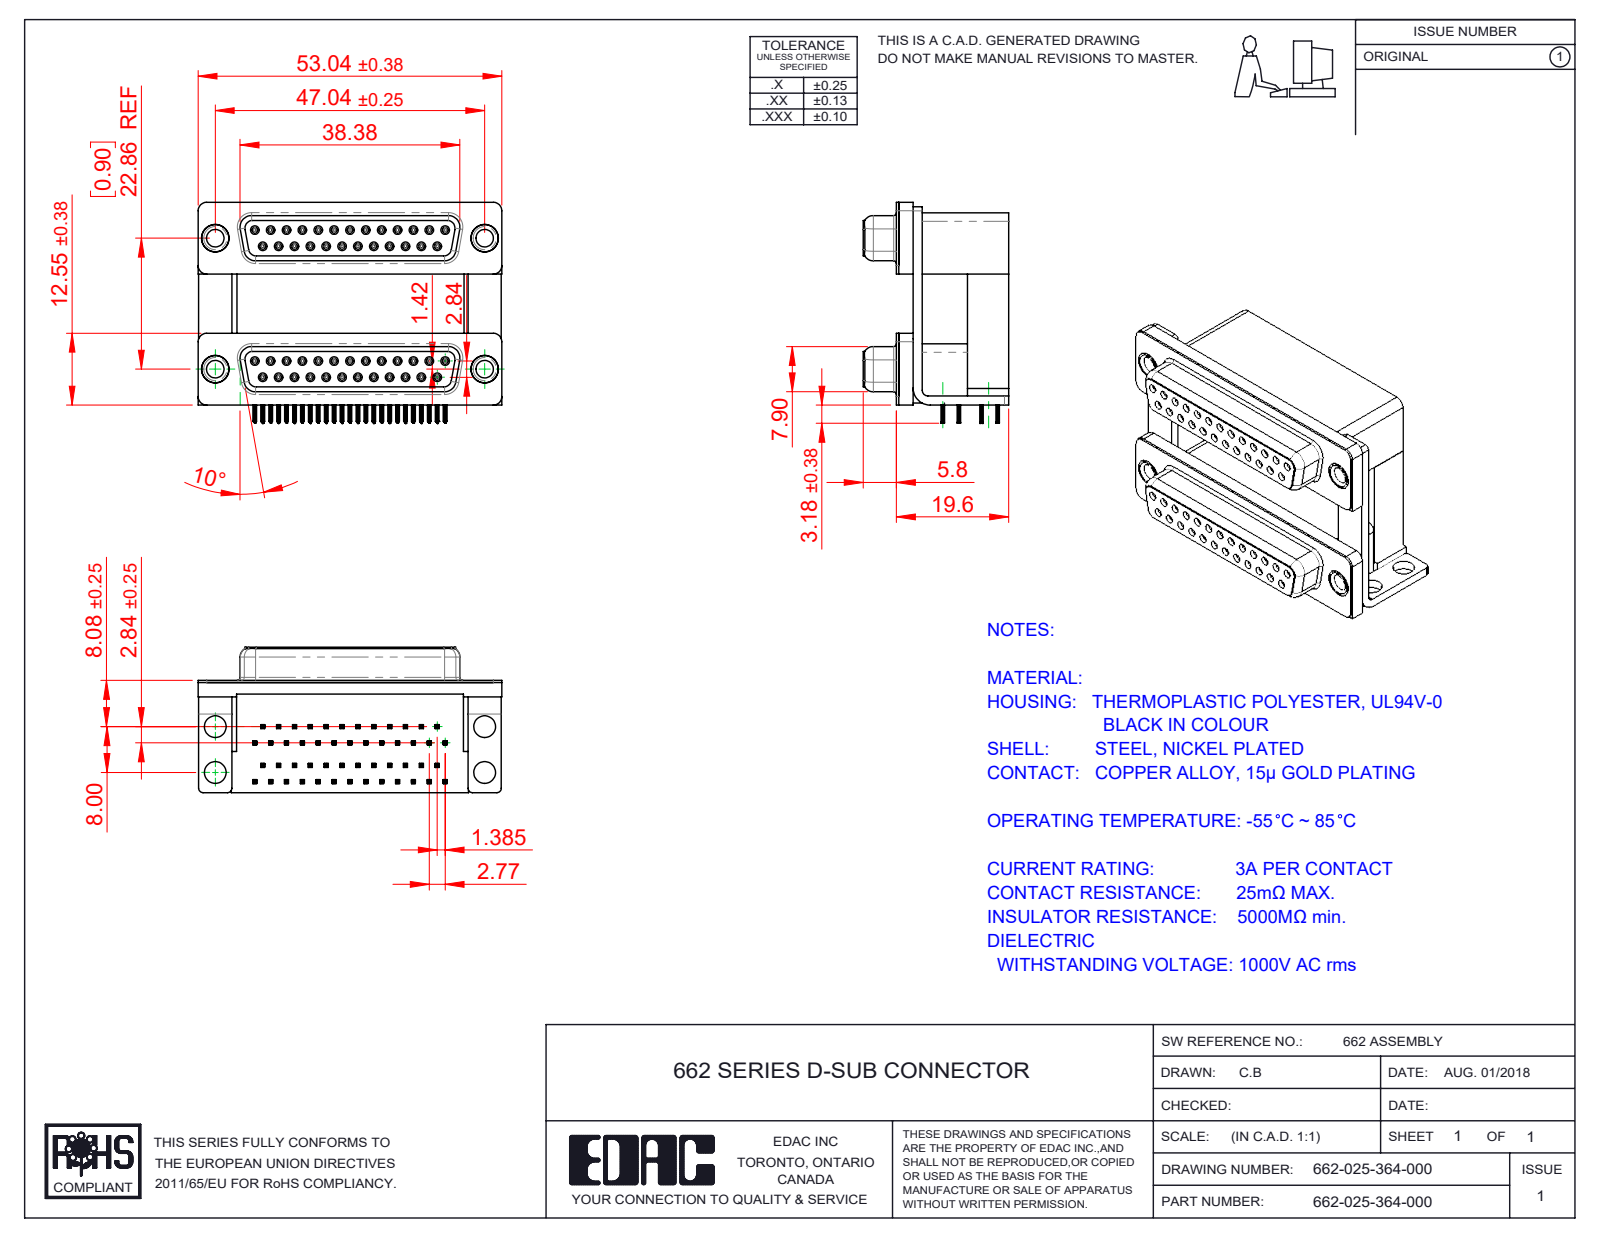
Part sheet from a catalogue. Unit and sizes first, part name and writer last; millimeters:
Units: millimetres
Overall size (bounding box): 53.04 × 38.59 × 25.4
Round holes (diameter × count): ⌀0.8 ×50, ⌀0.9 ×50, ⌀3.05 ×4, ⌀3.5 ×4, ⌀3.8 ×4, ⌀4 ×4, ⌀4.8 ×4, ⌀5 ×4
Round bosses / shafts (diameter × count): ⌀1.2 ×50, ⌀4.9 ×4, ⌀4.75 ×4, ⌀3.85 ×4
Partial cylindrical surfaces — rounded edges, fillets, slot ends (radius × count): R0.1 ×400, R0.15 ×200, R0.35 ×100, R0.34 ×50, R0.28 ×24, R1.35 ×16, R1.5 ×14, R0.5 ×8
Main face-to-face distances: 22.86, 19.2, 7.2, 12, 0.4, 10.7, 2.84, 6.2, 9.5, 16.7
Hole centre spacings: 3.16, 2.77, 5.54, 11.08, 8.31, 5.03, 13.85, 7.48
Volume: 24 938 mm³ · Surface area: 26 800 mm²
Bodies: 61 solids, 7708 faces (3576 planar, 1768 cylindrical, 2364 other)
Part name (STEP PRODUCT): 662 Thru Hole Rivet; 662 Contact Bottom Upper_H; 662 Mounting Bracket_NoneH; 662 Housing Upper_25 Contacts H (+7 more)
STEP written by: SolidWorks 2020 (CONFIG_CONTROL_DESIGN)
